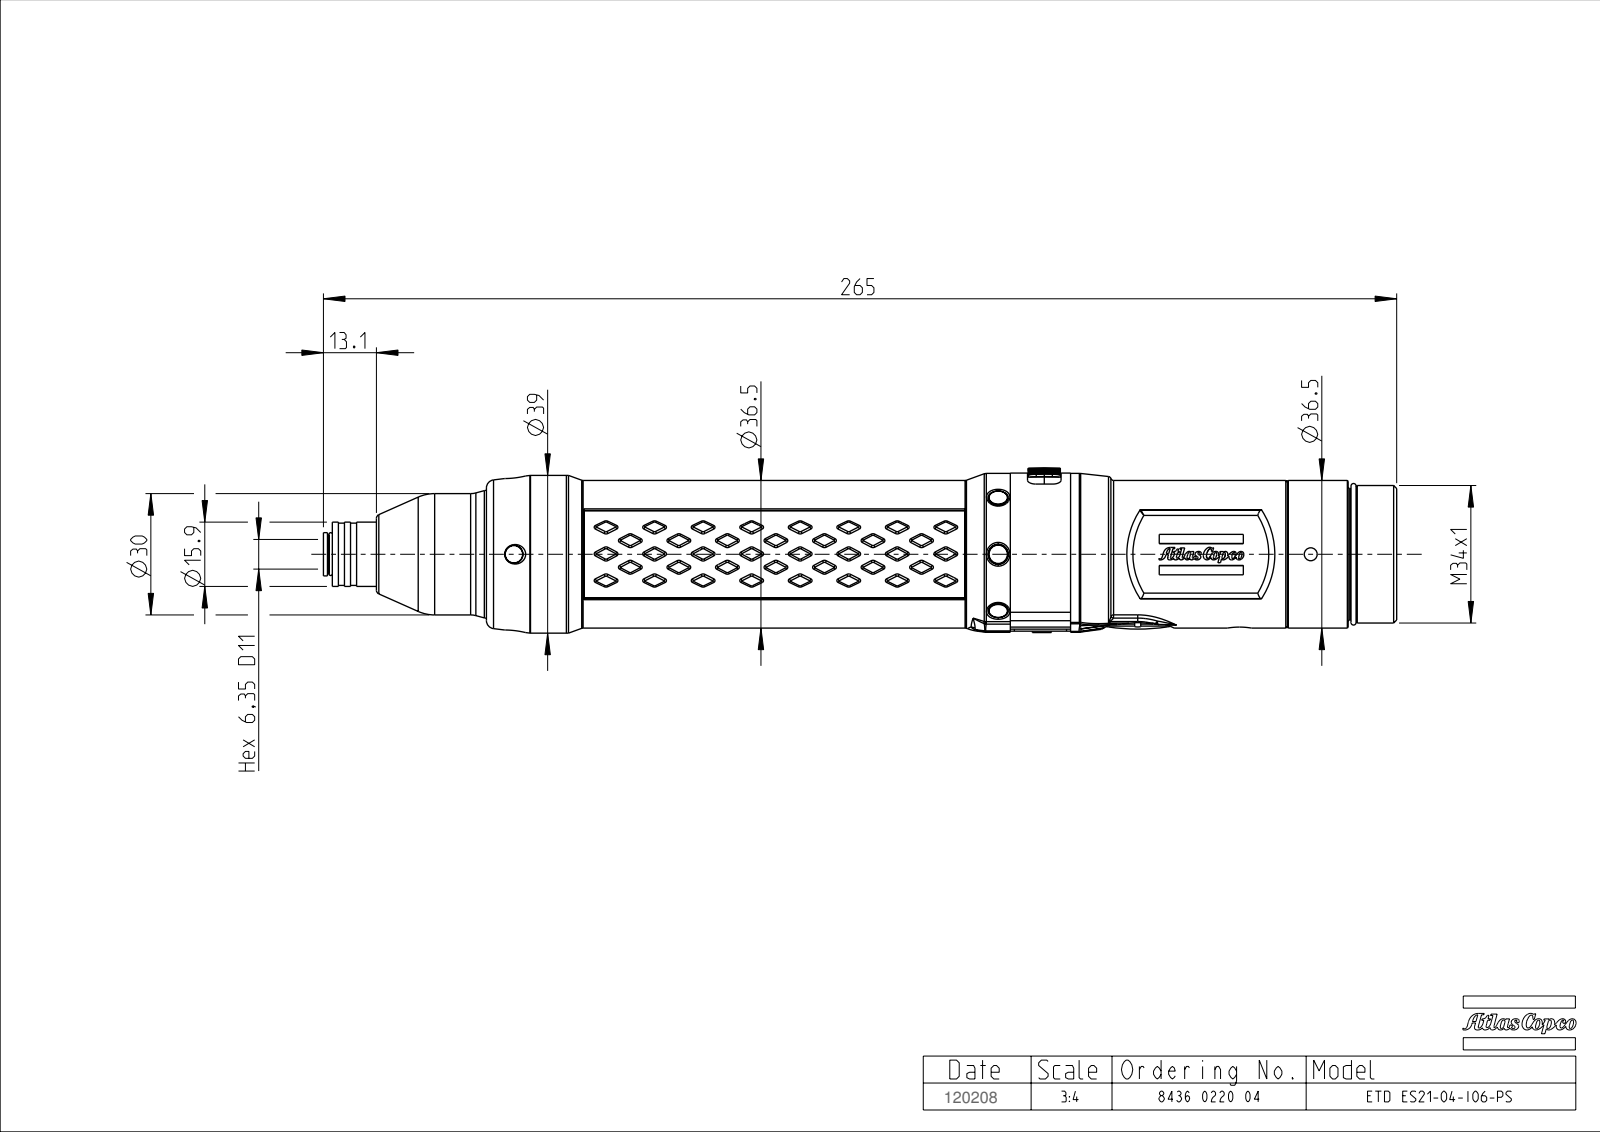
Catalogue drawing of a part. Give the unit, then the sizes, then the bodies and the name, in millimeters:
Units: millimetres
Overall size (bounding box): 265.35 × 40.82 × 40.15
Round holes (diameter × count): ⌀7.5 ×1, ⌀37 ×1
Round bosses / shafts (diameter × count): ⌀1.57 ×8, ⌀40 ×1, ⌀39 ×1, ⌀36.5 ×1, ⌀34 ×1, ⌀33.5 ×1, ⌀30 ×1, ⌀18 ×1
Partial cylindrical surfaces — rounded edges, fillets, slot ends (radius × count): R3 ×9, R1 ×3, R0.1 ×2, R0.2 ×2, R0.25 ×2, R5 ×2, R6 ×2, R9.5 ×2
Main face-to-face distances: 6.34, 0.38, 18.72, 19.1, 263.15, 244.43, 244.05, 12, 6.72, 7.1
Bodies: 0 solids, 791 faces (163 planar, 185 cylindrical, 443 other)
Part name (STEP PRODUCT): TMP14757_SW
STEP written by: PRO/ENGINEER BY PARAMETRIC TECHNOLOGY CORPORATION, 2008310 (CONFIG_CONTROL_DESIGN)
